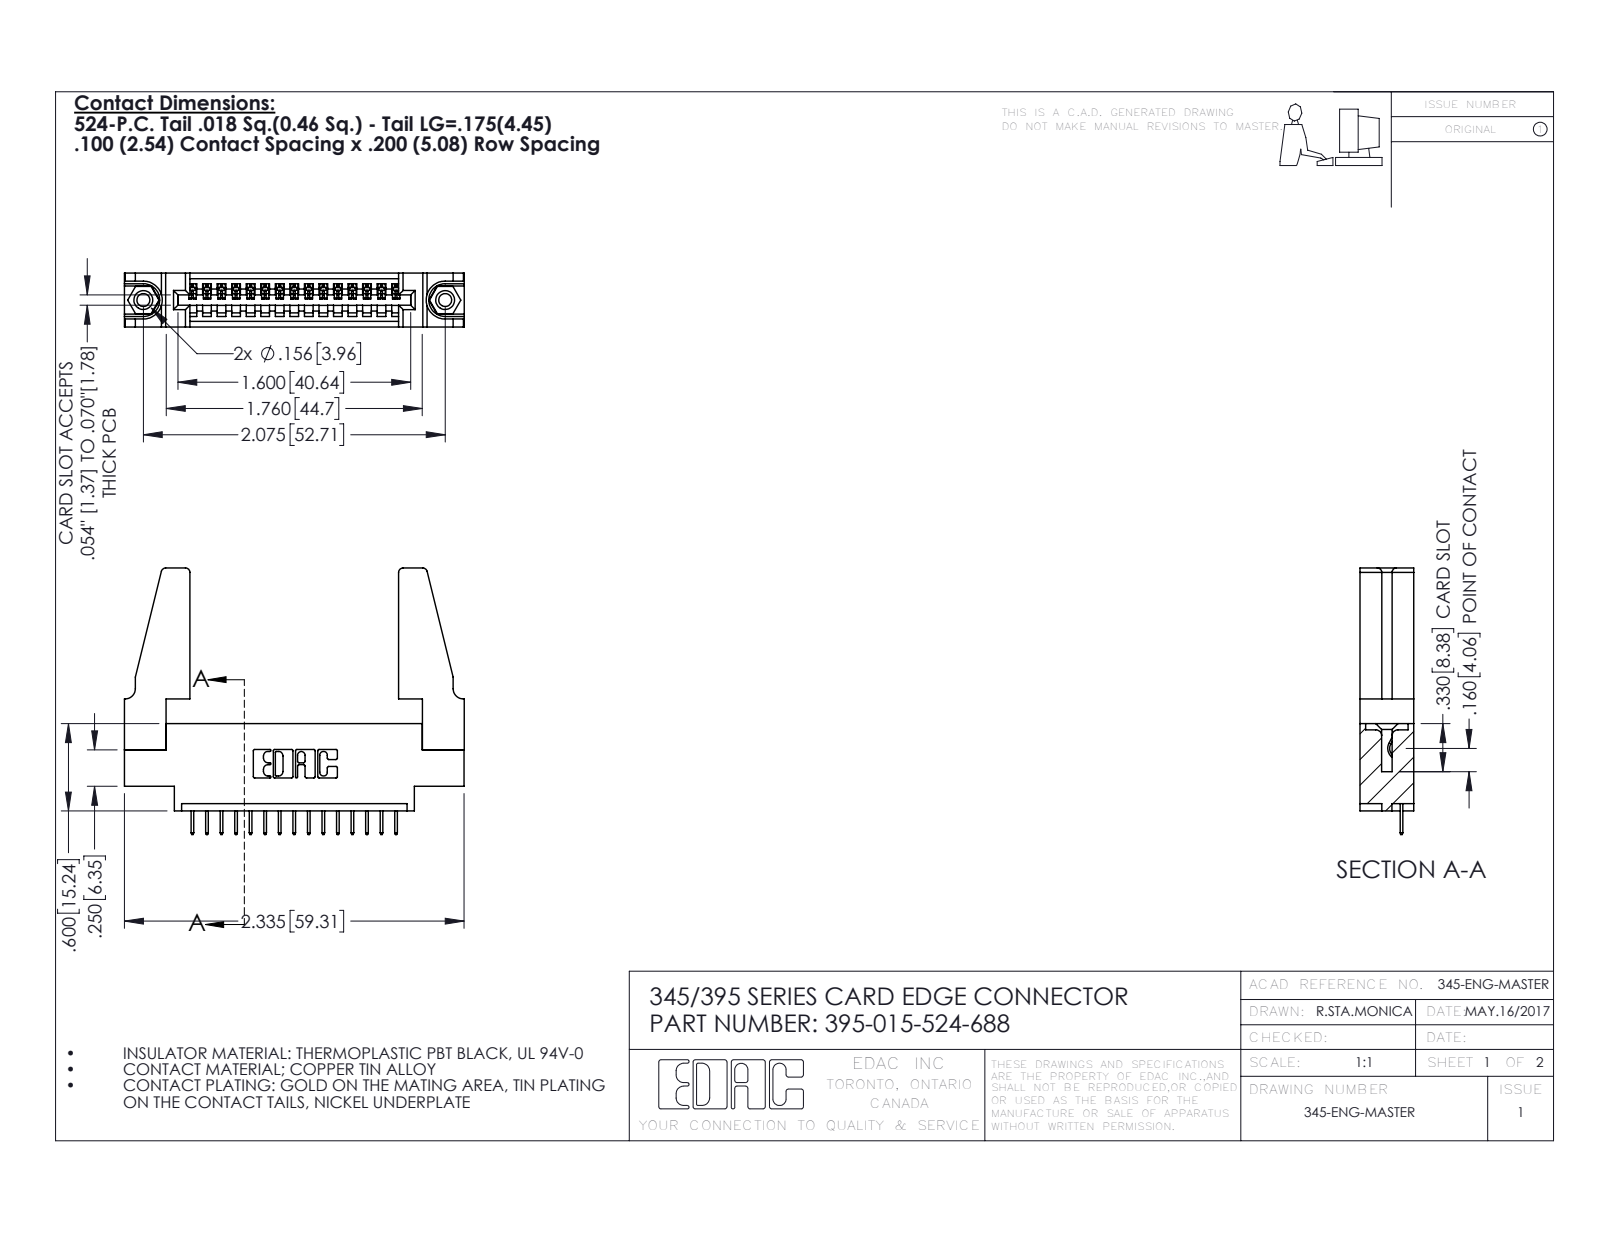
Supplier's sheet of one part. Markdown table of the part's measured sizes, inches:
| quantity | value |
| --- | --- |
| part name | 345 Part_0.170 Offset - 0.156 Dia-TH; 345-220-078_345-220-088; 345-250-001_345-250-001-102; 345-292-001_345-293-124 (+1 more) |
| STEP written by | SolidWorks 2016 (CONFIG_CONTROL_DESIGN) |
| units | inches |
| bodies | 20 solids, 1184 faces (846 planar, 322 cylindrical, 16 other) |
| overall size | 2.336 × 1.832 × 0.37 |
| volume | 0.518 in³ |
| surface area | 14.98 in² |
| round holes (diameter × count) | 0.089 × 2, 0.125 × 2, 0.156 × 2, 0.064 × 1 |
| round bosses / shafts (diameter × count) | 0.155 × 2 |
| partial cylindrical surfaces (radius × count) | 0.006 × 30, 0.01 × 22, 0.03 × 8, 0.007 × 6, 0.031 × 6, 0.026 × 3, 0.031 × 2, 0.04 × 2 |
| main face-to-face distances | 0.37, 0.072, 0.298, 0.2, 0.098, 0.272, 0.025, 0.225, 0.148, 0.15 |
| hole center spacings | 0.27, 1.842, 2.075 |
